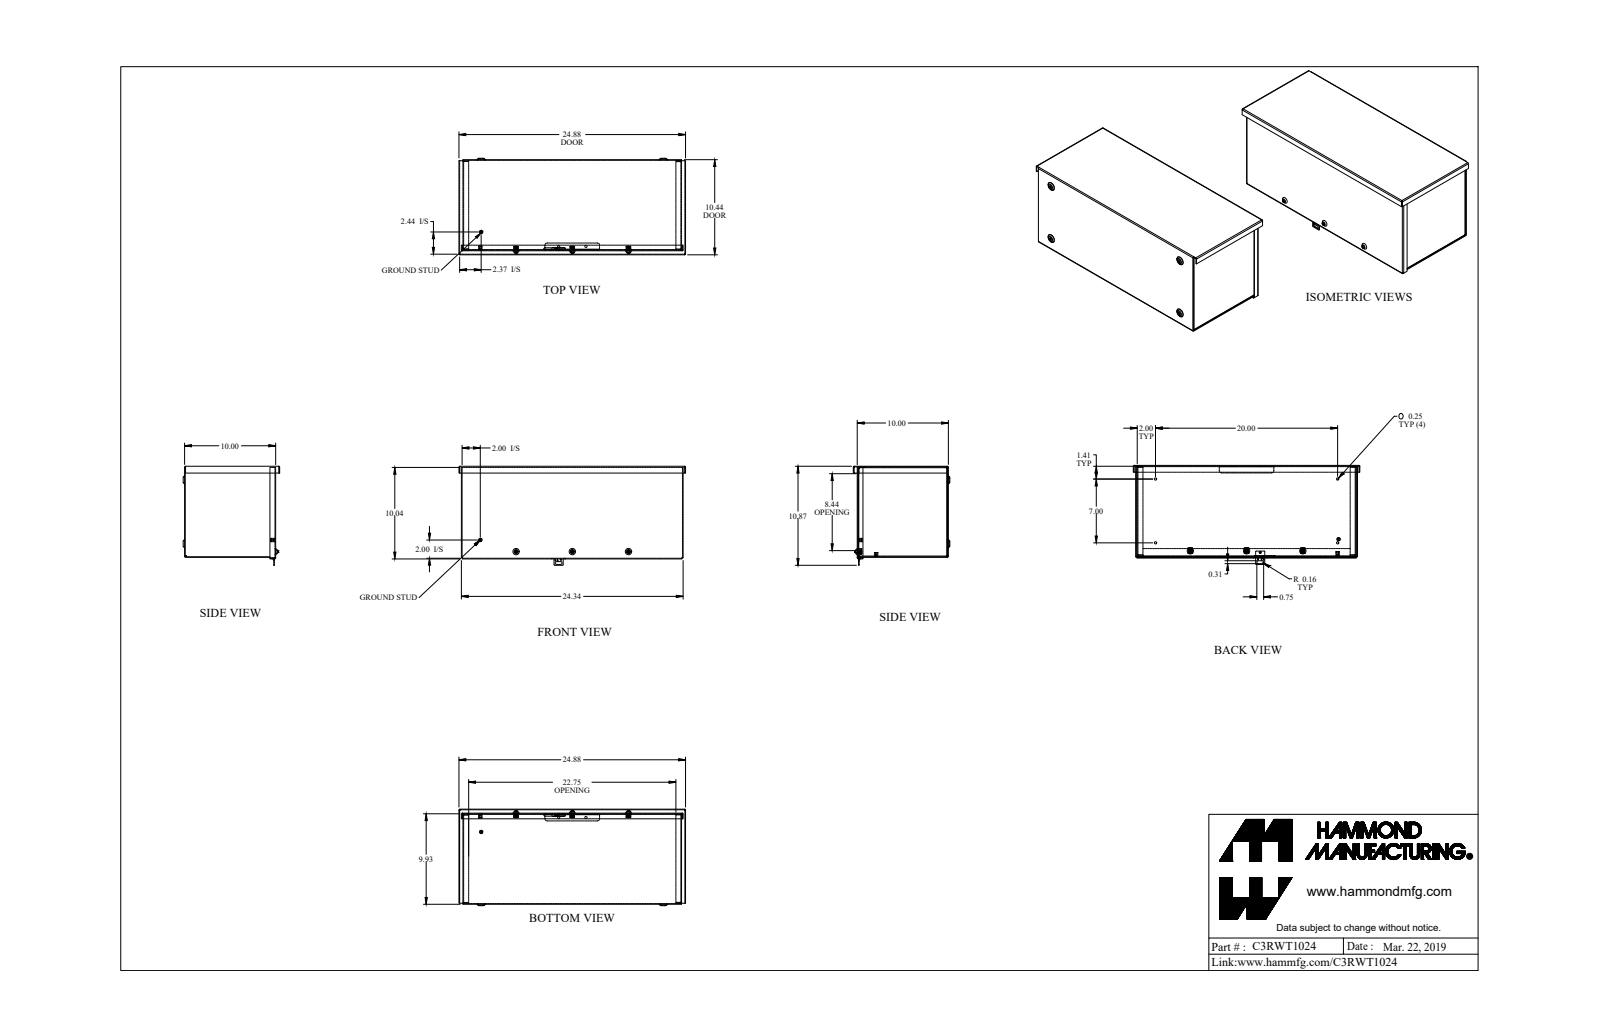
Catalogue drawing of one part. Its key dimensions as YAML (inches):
part_name: "C3RWT1024_Default"
step_written_by: "SolidWorks 2019 (CONFIG_CONTROL_DESIGN)"
units: inches
bodies: {solids: 22, faces: 764, planar: 415, cylindrical: 237, other: 112}
overall_size: [24.875, 10.871, 10.594]
volume: 93.35
surface_area: 2621
round_holes:
  - {diameter: 0.25, count: 6}
  - {diameter: 0.156, count: 5}
  - {diameter: 0.214, count: 3}
  - {diameter: 0.23, count: 3}
  - {diameter: 0.203, count: 2}
  - {diameter: 0.125, count: 1}
  - {diameter: 0.137, count: 1}
  - {diameter: 0.2, count: 1}
  - {diameter: 0.215, count: 1}
round_bosses_or_shafts:
  - {diameter: 0.19, count: 4}
  - {diameter: 0.148, count: 3}
  - {diameter: 0.375, count: 2}
  - {diameter: 0.5, count: 1}
  - {diameter: 0.367, count: 1}
  - {diameter: 0.21, count: 1}
  - {diameter: 0.152, count: 1}
  - {diameter: 0.125, count: 1}
partial_cylinders:
  - {radius: 0.036, count: 18}
  - {radius: 0.108, count: 18}
  - {radius: 0.08, count: 12}
  - {radius: 0.108, count: 12}
  - {radius: 0.125, count: 11}
  - {radius: 0.022, count: 6}
  - {radius: 0.25, count: 6}
  - {radius: 0.016, count: 4}
face_to_face_distances: [0.072, 9.928, 9.856, 10, 23.928, 24, 23.856, 0.172, 0.144, 9.784]
hole_center_spacings: [4.928, 16.898, 3.927, 4.389, 6.172, 7, 7.861, 8.756]
